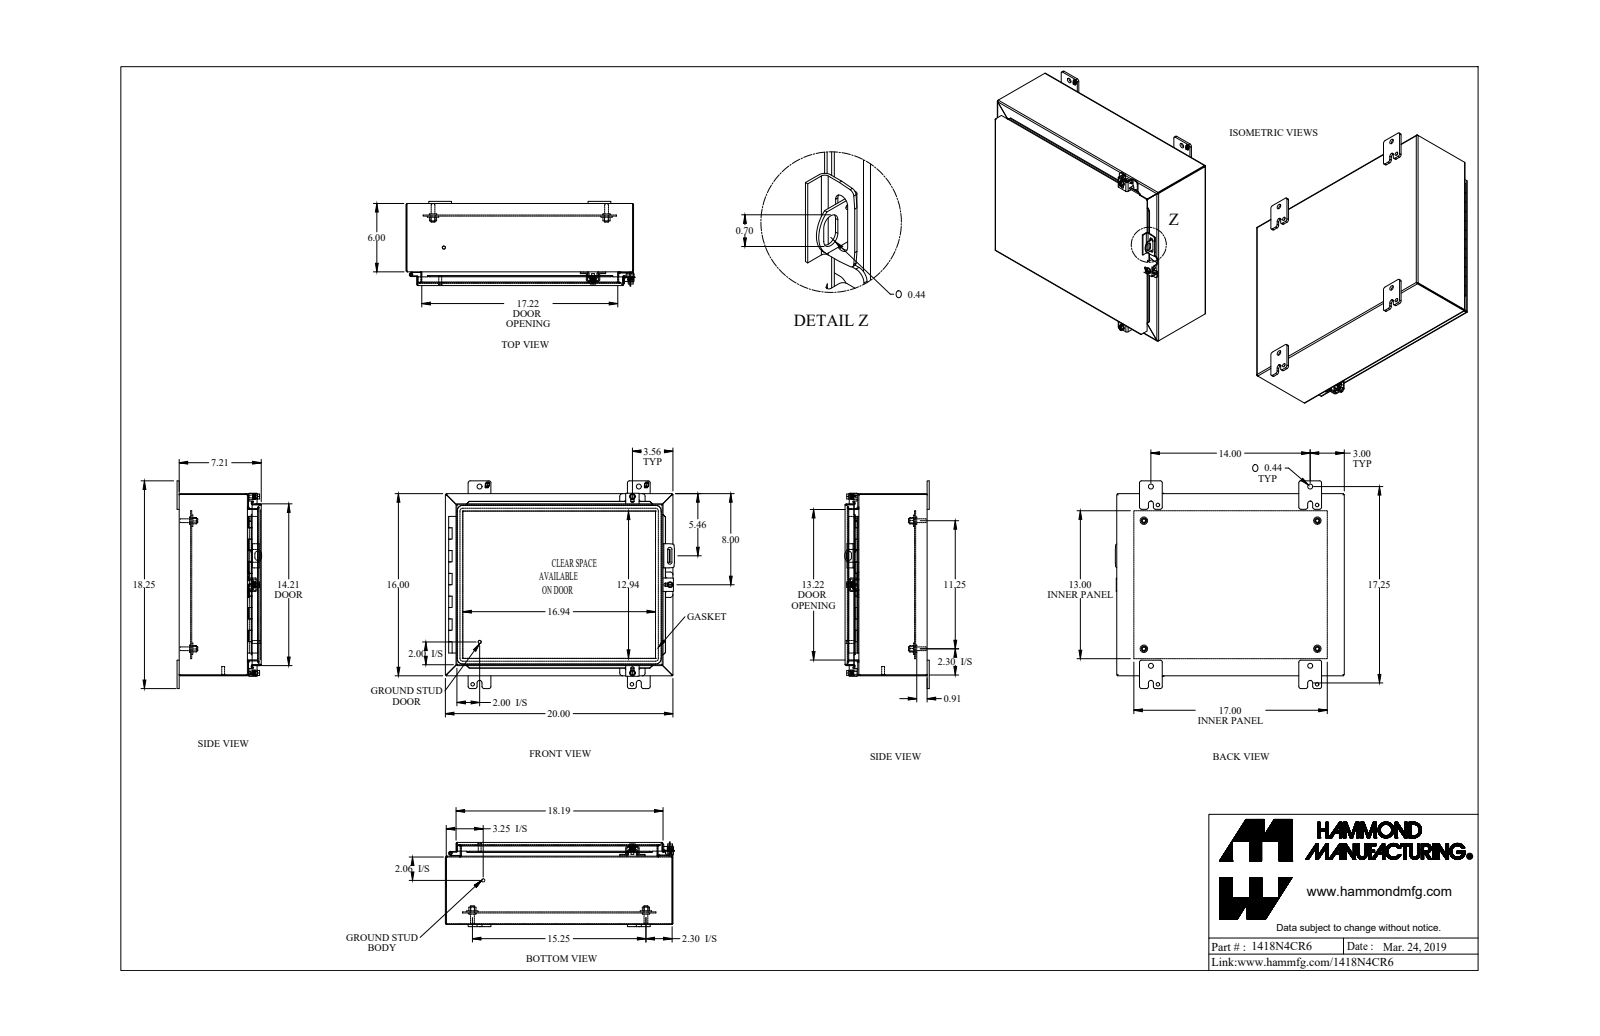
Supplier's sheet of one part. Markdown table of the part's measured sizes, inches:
| quantity | value |
| --- | --- |
| part name | 1418N4CR6_Default |
| STEP written by | SolidWorks 2019 (CONFIG_CONTROL_DESIGN) |
| units | inches |
| bodies | 35 solids, 1197 faces (729 planar, 386 cylindrical, 82 other) |
| overall size | 20.126 × 18.25 × 7.437 |
| volume | 122 in³ |
| surface area | 3 196 in² |
| round holes (diameter × count) | 0.313 × 4, 0.437 × 4, 0.5 × 4, 0.213 × 3, 0.265 × 3, 0.375 × 3, 0.307 × 2, 0.445 × 2, 0.125 × 1, 0.187 × 1 |
| round bosses / shafts (diameter × count) | 0.65 × 4, 0.375 × 4, 0.33 × 4, 0.5 × 3, 0.39 × 3, 0.244 × 3, 1 × 2, 0.281 × 2 |
| partial cylindrical surfaces (radius × count) | 0.188 × 26, 0.036 × 24, 0.108 × 24, 0.25 × 16, 0.048 × 15, 0.143 × 15, 0.045 × 8, 0.125 × 8 |
| main face-to-face distances | 0.072, 0.072, 7.066, 7.138, 7.138, 7.21, 15.928, 0.095, 6.106, 6.034 |
| hole center spacings | 18.951, 14, 15.25, 18.263, 20.42, 1.625, 1.735, 1.736 |
